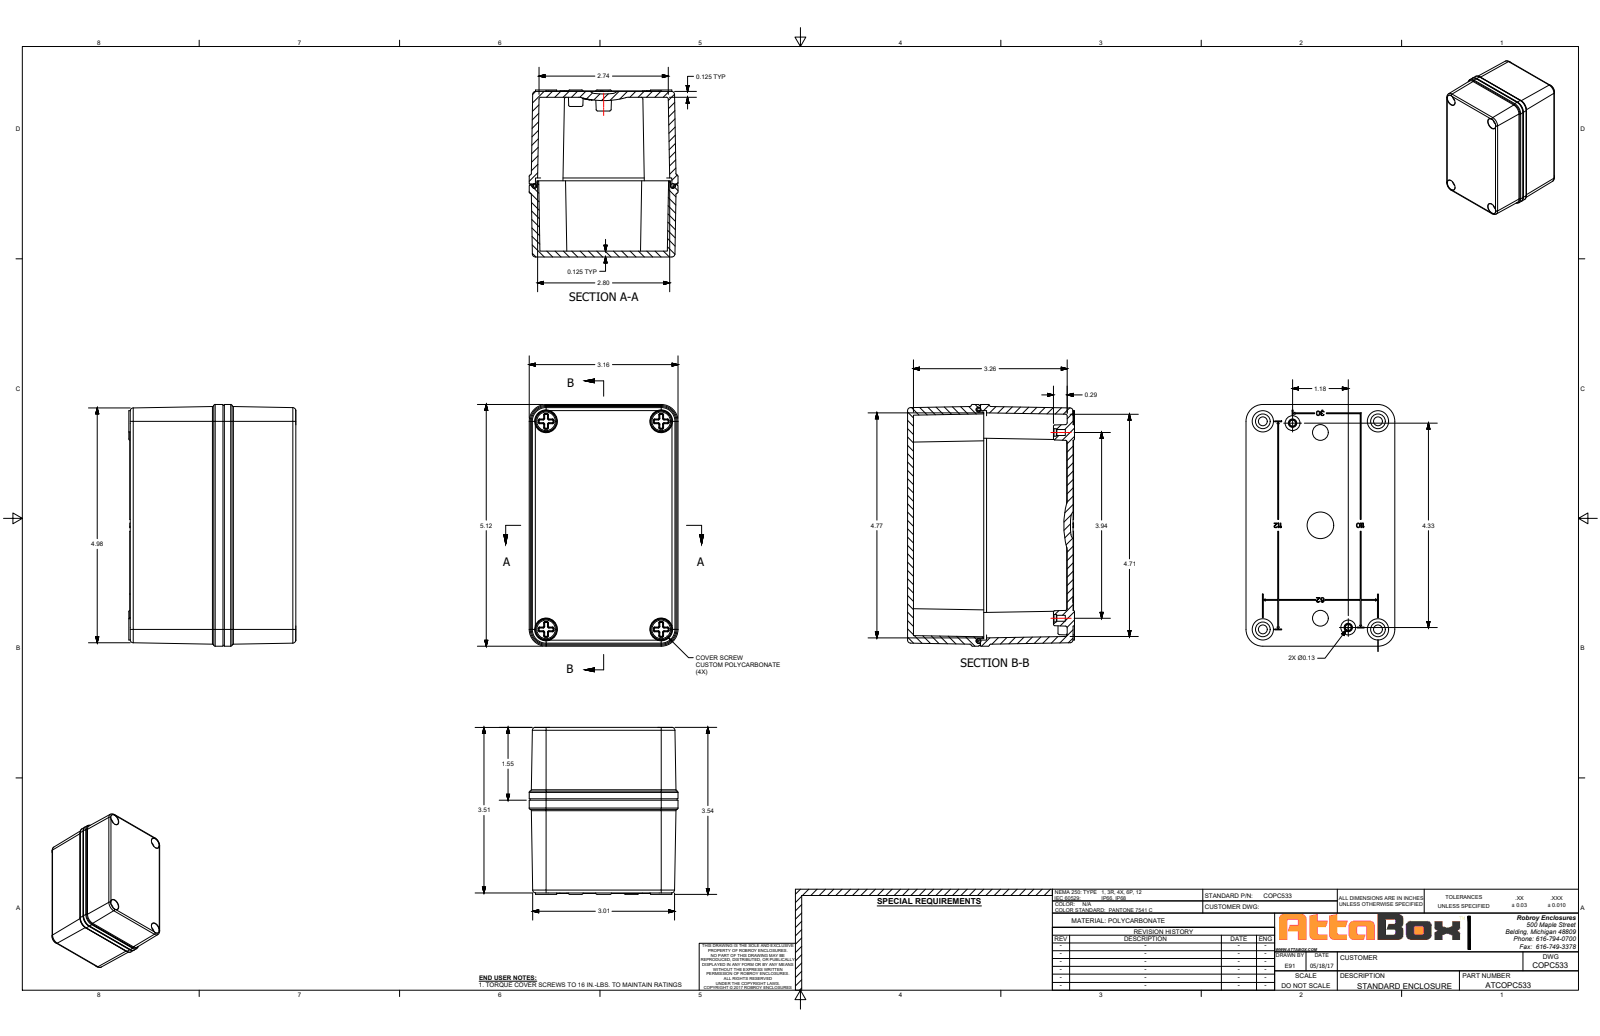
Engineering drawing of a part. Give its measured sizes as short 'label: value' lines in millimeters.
name: COPC533
written by: SolidWorks 2018 (AUTOMOTIVE_DESIGN)
unit: mm
bodies: 7 solids, 1097 faces (251 planar, 465 cylindrical, 381 other)
size: 130.1 × 89.9 × 80.1
volume: 219 600 mm³; area: 128 000 mm²
holes: 6× ⌀2.5, 4× ⌀4.7, 4× ⌀8, 4× ⌀11.7, 3× ⌀12.6, 2× ⌀4, 1× ⌀12.6
bosses: 4× ⌀11.4, 4× ⌀11, 4× ⌀7, 2× ⌀8.5, 2× ⌀8.5, 2× ⌀8, 2× ⌀7.9, 2× ⌀2.5
rounds: 48× R0.5, 32× R0.3, 14× R0.4, 12× R0.5, 8× R0.8, 8× R1, 8× R2, 8× R3.8
face distances: 4.1, 89.2, 3.2, 86, 86, 82.8, 3.2, 71.1, 4.5, 49.9
hole spacings: 14.5, 16, 46, 62, 110.1, 112, 112.1, 120.1
